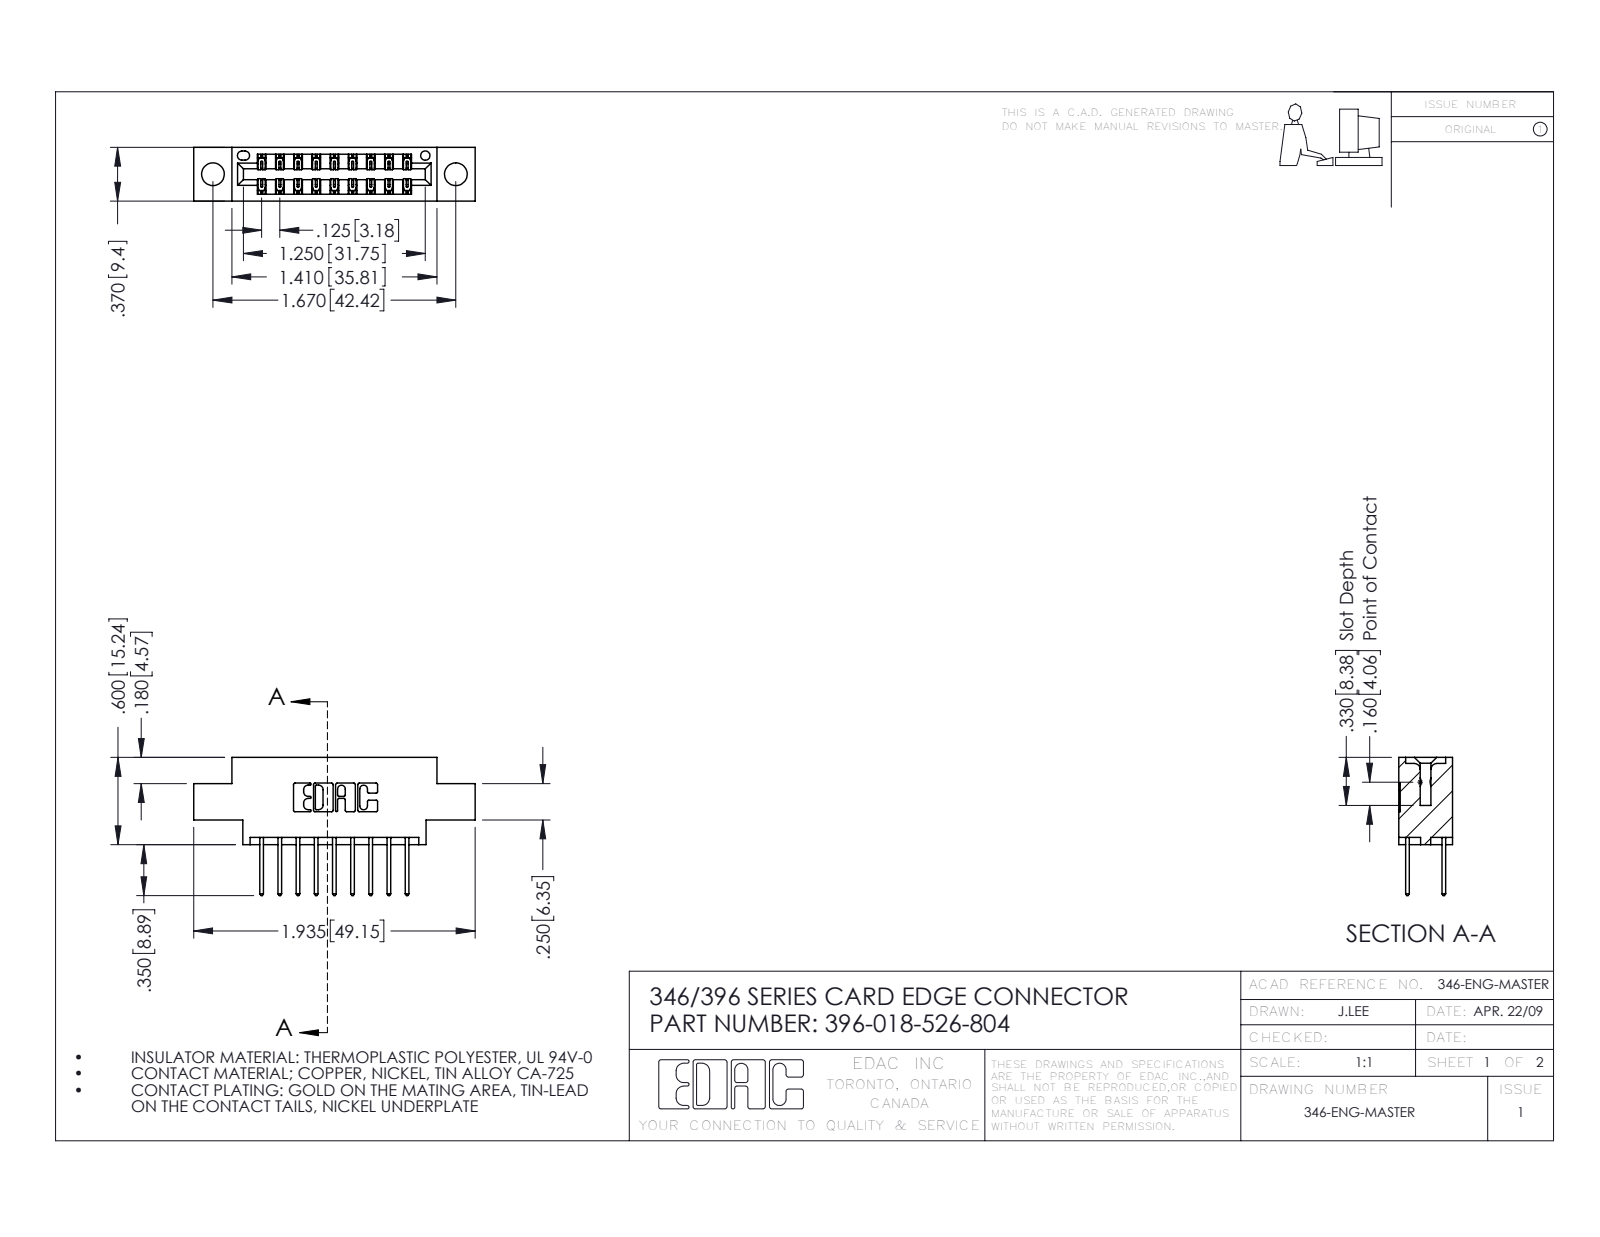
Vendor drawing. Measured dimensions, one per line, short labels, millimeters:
name: 345-292-001_345-293-126; 396-018-526-804; 346 Part_0.170 Offset - 0.156 Dia-TH
written by: SolidWorks 2016 (CONFIG_CONTROL_DESIGN)
unit: mm
bodies: 19 solids, 1062 faces (710 planar, 352 cylindrical, 0 other)
size: 49.1 × 24.1 × 9.4
volume: 4 330 mm³; area: 5 549 mm²
holes: 2× ⌀4, 1× ⌀1.6
rounds: 27× R0.2, 22× R0.3, 18× R0.3, 6× R0.2, 6× R0.8, 3× R0.7, 2× R0.4, 2× R0.6
face distances: 6.4, 1.2, 8.2, 9.4, 1.8, 7.6, 0.6, 7, 3.8, 5.6
hole spacings: 6.2, 37.2, 42.4
